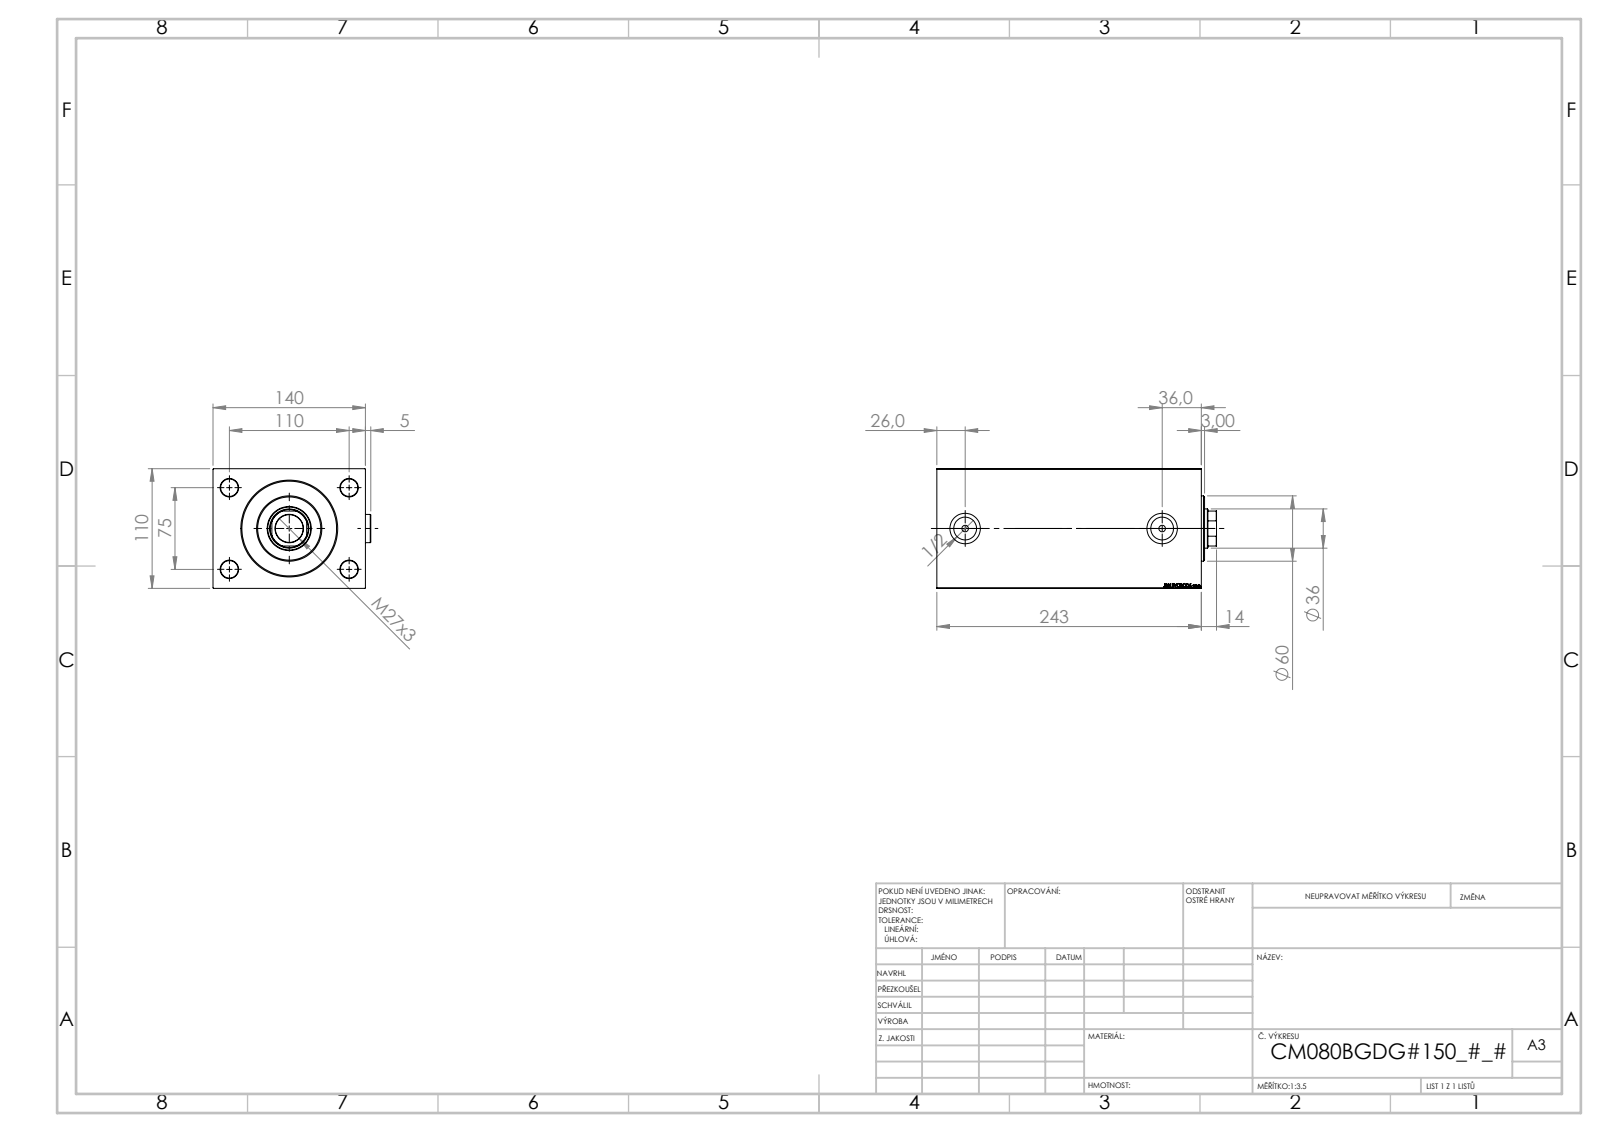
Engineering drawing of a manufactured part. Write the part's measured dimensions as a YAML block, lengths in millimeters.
part_name: "V450CM_B_VCP; Zatka_OIL_PORT; V450CM_B_Body; V450CM_VC_B"
step_written_by: "SolidWorks 2019 (CONFIG_CONTROL_DESIGN)"
units: millimeters
bodies: {solids: 4, faces: 89, planar: 47, cylindrical: 26, other: 16}
overall_size: [244, 118.4, 87]
volume: 527037
surface_area: 66303
round_holes:
  - {diameter: 25.5, count: 1}
  - {diameter: 36, count: 1}
  - {diameter: 39.5, count: 1}
  - {diameter: 40.5, count: 1}
round_bosses_or_shafts:
  - {diameter: 26, count: 2}
  - {diameter: 87, count: 1}
  - {diameter: 82, count: 1}
  - {diameter: 80, count: 1}
  - {diameter: 60, count: 1}
partial_cylinders:
  - {radius: 17.5, count: 1}
face_to_face_distances: [208, 150, 58, 14, 164, 222, 3, 5, 17, 167]
